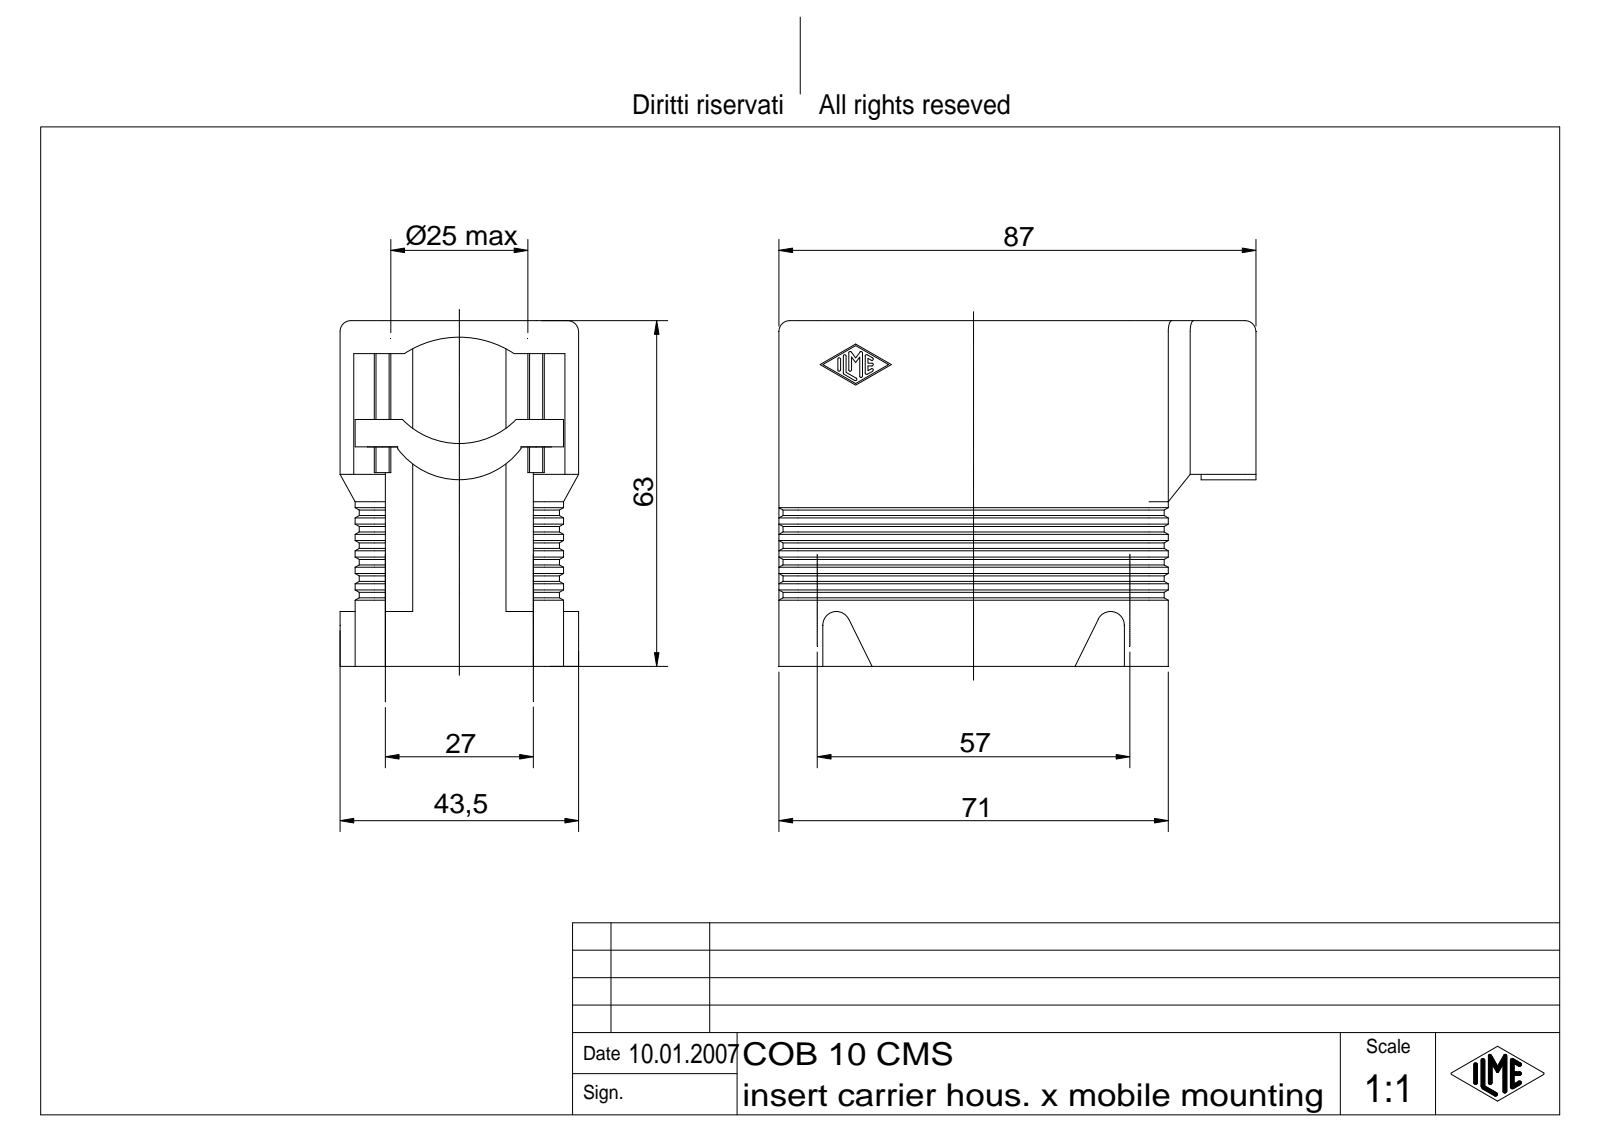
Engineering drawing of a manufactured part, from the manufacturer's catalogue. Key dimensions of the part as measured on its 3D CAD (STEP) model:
Part name (STEP PRODUCT): COB 10 CMS
STEP written by: Autodesk Inventor 7 (AUTOMOTIVE_DESIGN)
Units: millimetres
Bodies: 6 solids, 559 faces (217 planar, 147 cylindrical, 195 other)
Overall size (bounding box): 87 × 63 × 43.5
Volume: 44 254 mm³ · Surface area: 40 621 mm²
Round holes (diameter × count): ⌀3.5 ×4
Round bosses / shafts (diameter × count): ⌀3.49 ×4, ⌀5.2 ×1, ⌀3 ×1
Partial cylindrical surfaces — rounded edges, fillets, slot ends (radius × count): R0.25 ×14, R2 ×10, R1.5 ×4, R3.5 ×4, R4 ×4, R5 ×4, R0.5 ×2, R2.5 ×2
Main face-to-face distances: 2, 36, 38, 34, 3, 4.75, 35.25, 3.5, 2.75, 38.75
Hole centre spacings: 27, 57, 63.07
